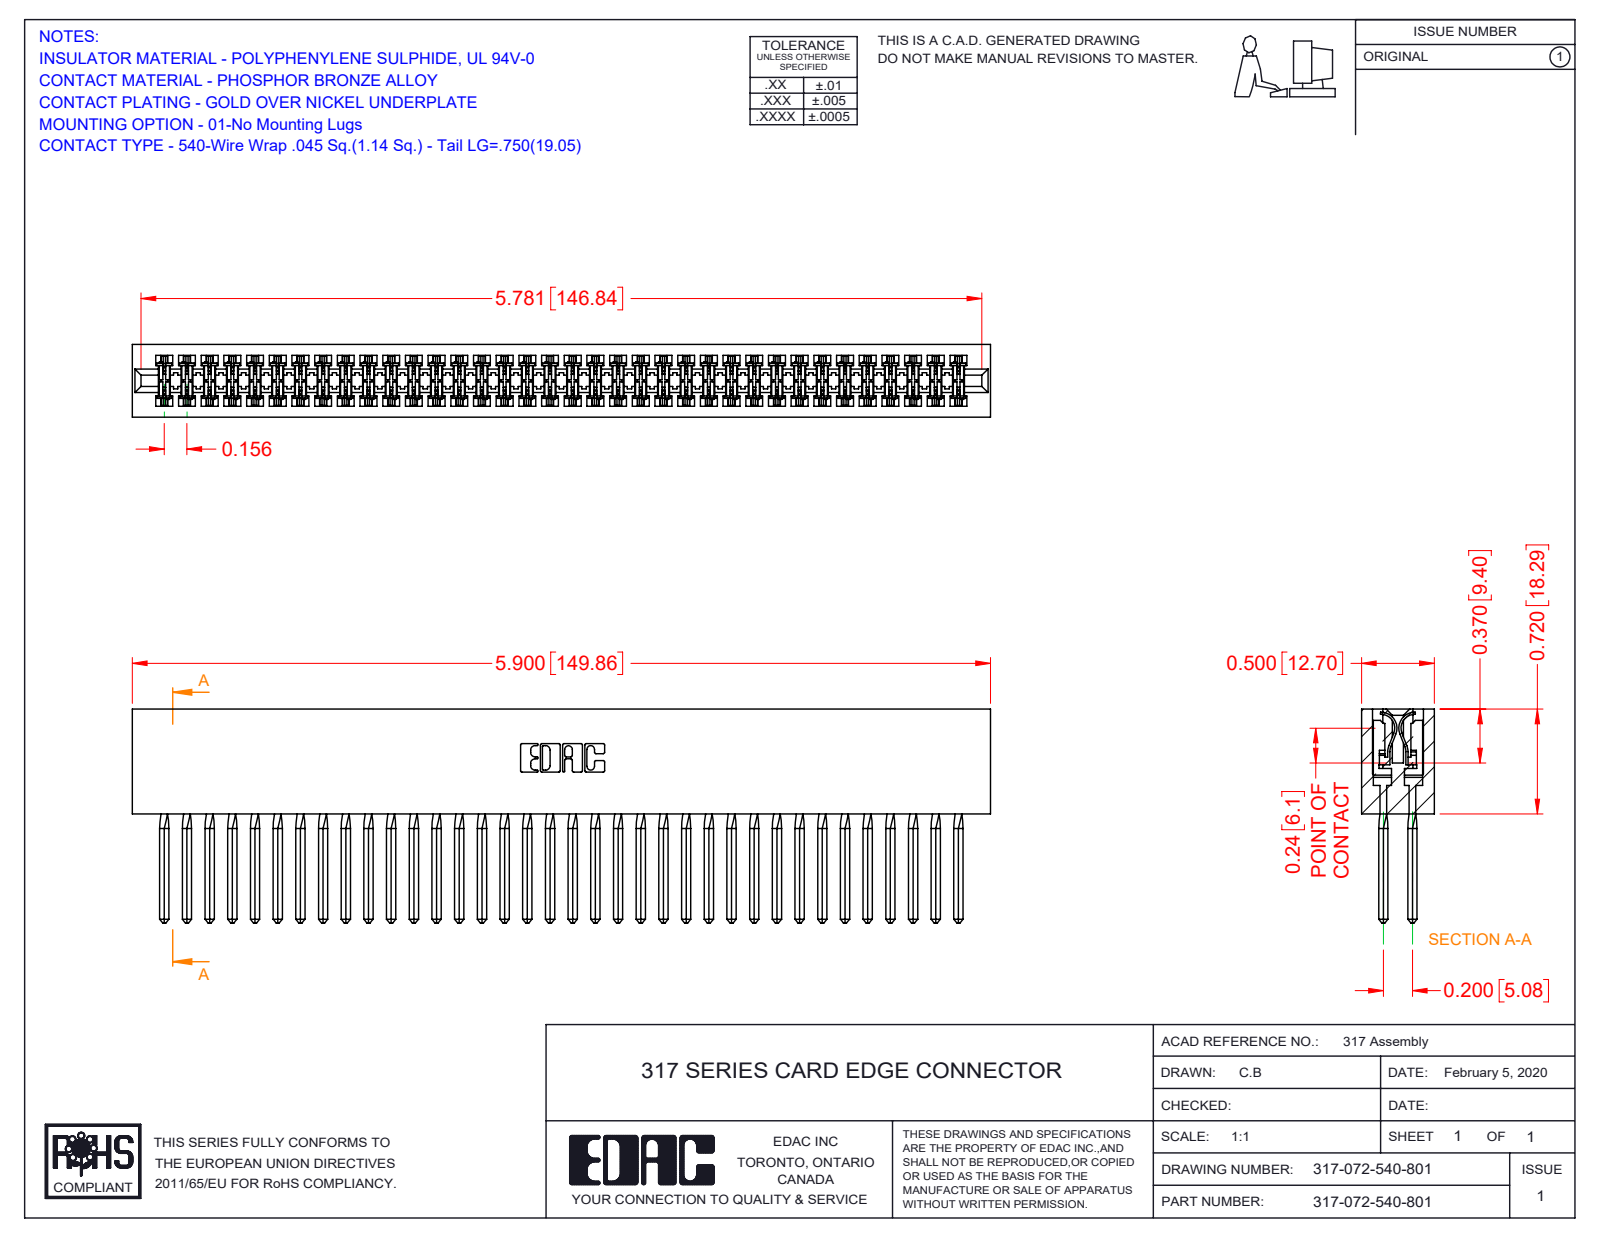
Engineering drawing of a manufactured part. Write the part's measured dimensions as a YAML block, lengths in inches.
part_name: "317-290-001_540; 317-072-540-801; 317 Part_Lugless"
step_written_by: "SolidWorks 2016 (CONFIG_CONTROL_DESIGN)"
units: inches
bodies: {solids: 73, faces: 6498, planar: 5306, cylindrical: 904, other: 288}
overall_size: [5.9, 1.47, 0.5]
volume: 1.632
surface_area: 61.84
partial_cylinders:
  - {radius: 0.015, count: 144}
  - {radius: 0.01, count: 22}
  - {radius: 0.007, count: 6}
  - {radius: 0.031, count: 6}
  - {radius: 0.026, count: 3}
  - {radius: 0.095, count: 2}
  - {radius: 0.1, count: 2}
  - {radius: 0.11, count: 2}
face_to_face_distances: [0.075, 0.5, 0.425, 0.35, 0.195, 0.11, 0.094, 0.2, 0.115, 0.131]
